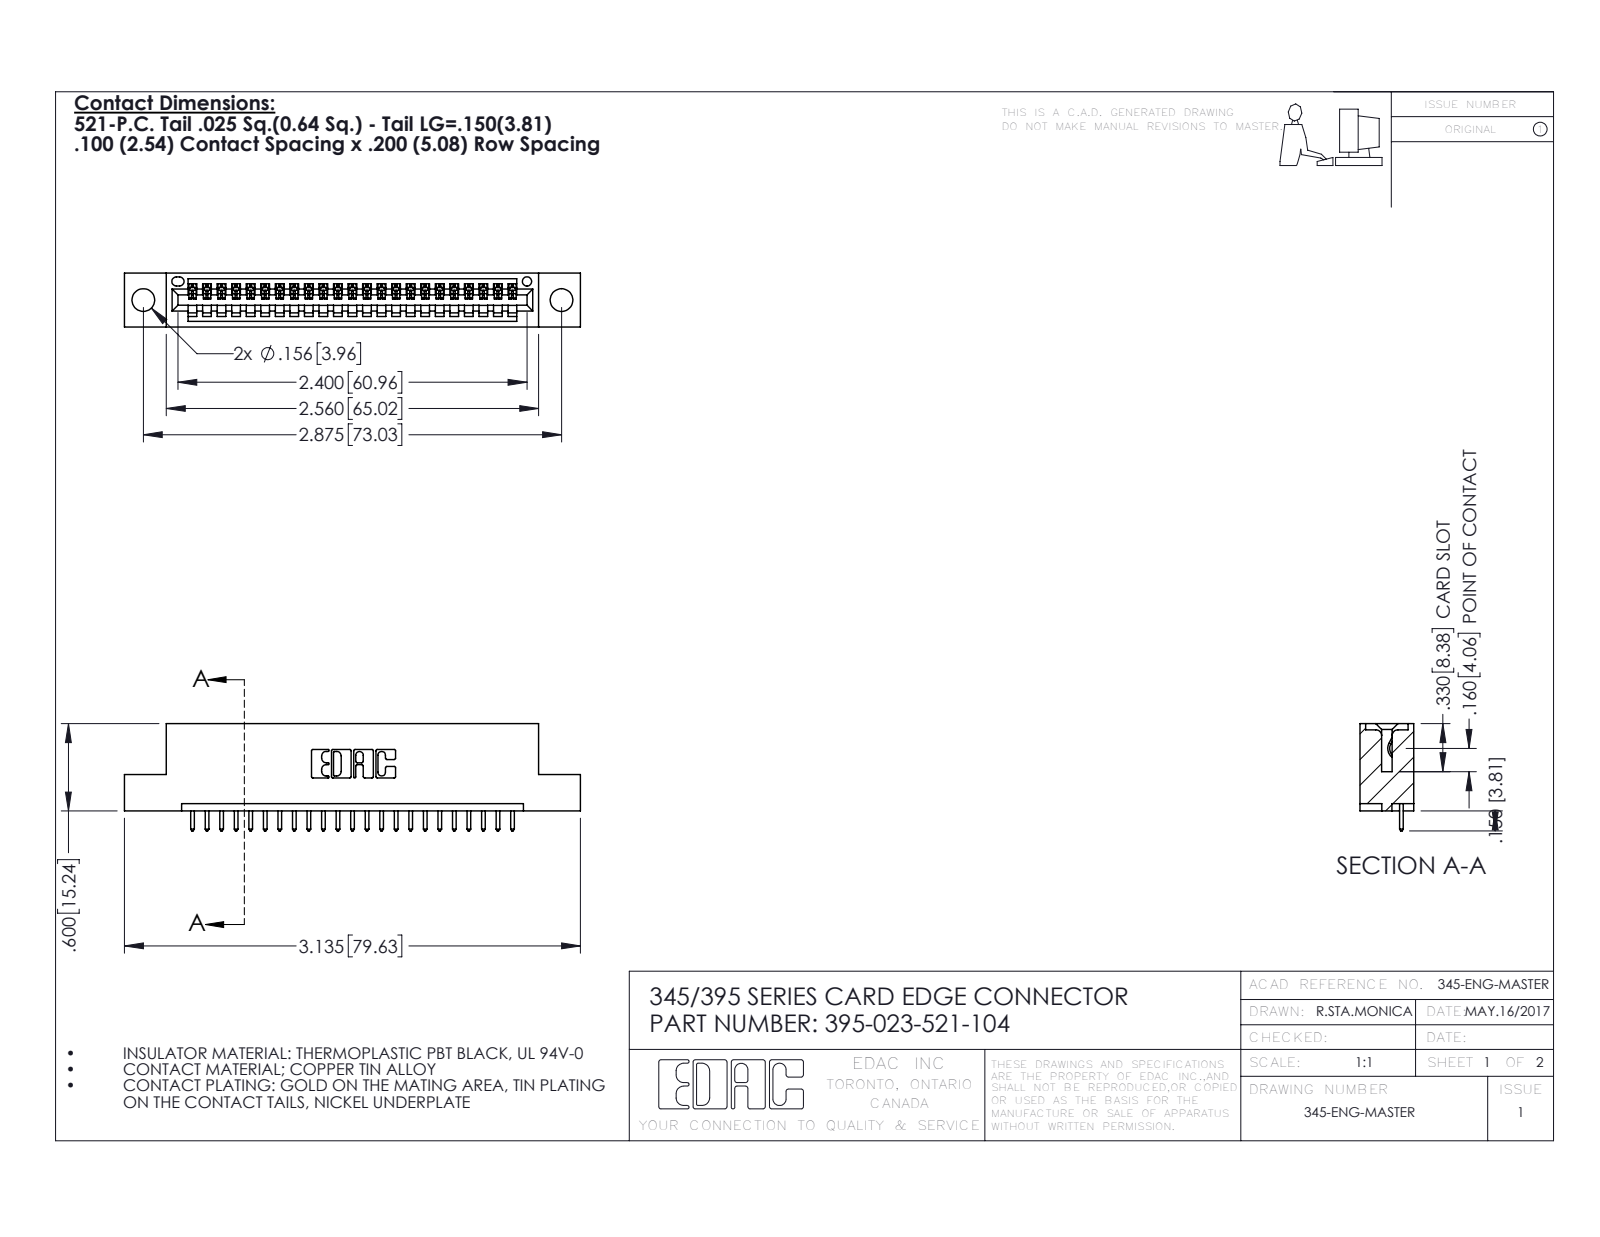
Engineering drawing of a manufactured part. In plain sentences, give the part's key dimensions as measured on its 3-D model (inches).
The part is named "395-023-521-104; 345-292-001_345-293-121; 345 Part_Flush Mounting Lugs - 0.156 Dia-TH". Its 3-D file was written by "SolidWorks 2016 (CONFIG_CONTROL_DESIGN)". It is 24 solids with 1460 faces: 1000 planar, 460 cylindrical and 0 other. Overall it measures 3.135 by 0.737 by 0.37 inches. Its volume is 0.443 cubic inches and its surface area 13.85 square inches. Round holes: 2 of diameter 0.156, 1 of diameter 0.064. Partial cylindrical surfaces (rounded edges, fillets, slot ends): 46 of radius 0.006, 46 of radius 0.01, 22 of radius 0.01, 6 of radius 0.007, 6 of radius 0.031, 3 of radius 0.026, 2 of radius 0.031, 2 of radius 0.04. The main face-to-face distances are 0.298, 0.072, 0.2, 0.37, 0.098, 0.272, 0.025, 0.225, 0.149, 0.072. The hole center spacings are 0.27, 2.641, 2.875.
